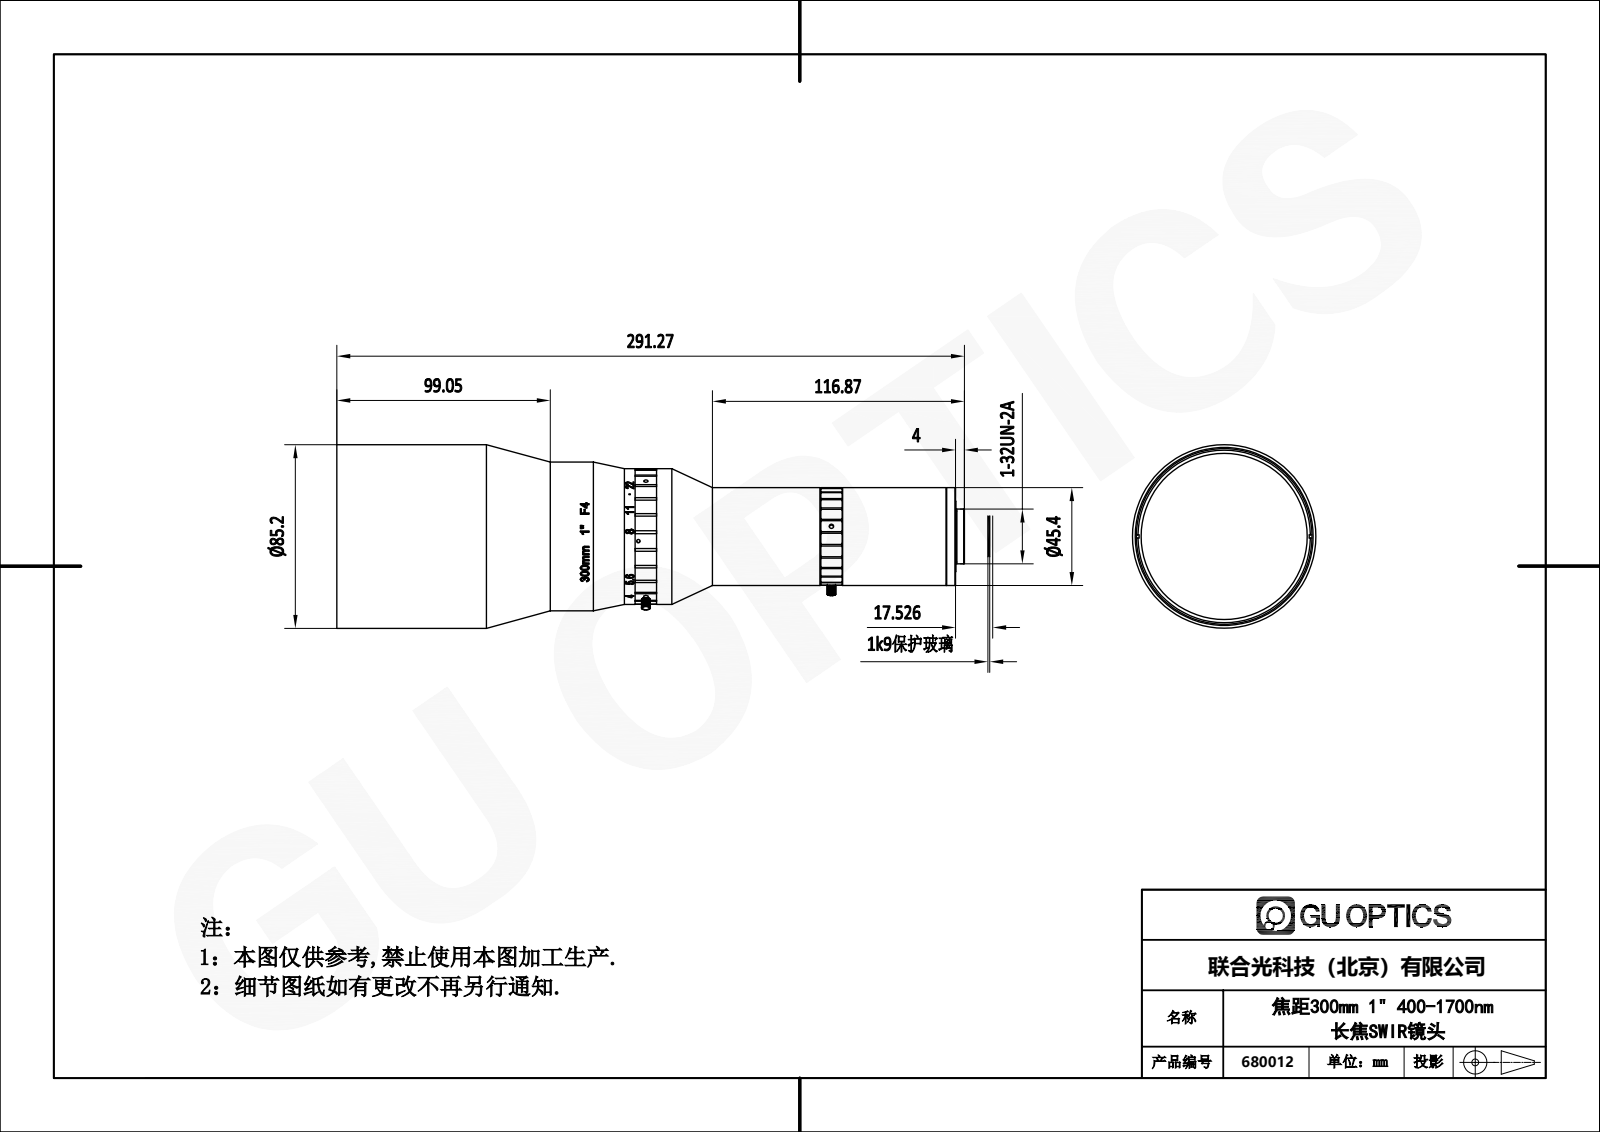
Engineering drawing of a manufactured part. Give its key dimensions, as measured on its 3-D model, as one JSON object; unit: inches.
{"part_name": "680012", "step_written_by": "SolidWorks 2020 (CONFIG_CONTROL_DESIGN)", "units": "inches", "bodies": {"solids": 19, "faces": 921, "planar": 346, "cylindrical": 251, "other": 324}, "overall_size": [11.467, 3.354, 3.354], "volume_in3": 58.98, "surface_area_in2": 205.4, "round_holes": [[0.079, 10], [0.081, 4], [0.112, 4], [0.039, 2], [0.764, 1], [0.843, 1], [1.173, 1], [1.528, 1], [1.591, 1], [1.685, 1], [1.728, 1], [1.748, 1]], "round_bosses_or_shafts": [[0.11, 4], [0.079, 4], [3.354, 1], [3.236, 1], [3.016, 1], [2.717, 1], [2.48, 1], [2.268, 1]], "partial_cylinders_radius": [[0.394, 24], [0.591, 24], [0.079, 2], [0.594, 1], [1.236, 1], [1.354, 1]], "face_to_face_distances": [4.975, 0.315, 3.706, 8.681, 10.366, 5.391, 1.685, 4.66, 4.021, 5.706], "hole_center_spacings": [0.705, 0.996, 0.624, 1.032, 1.22, 0.376, 0.48, 1.146]}
